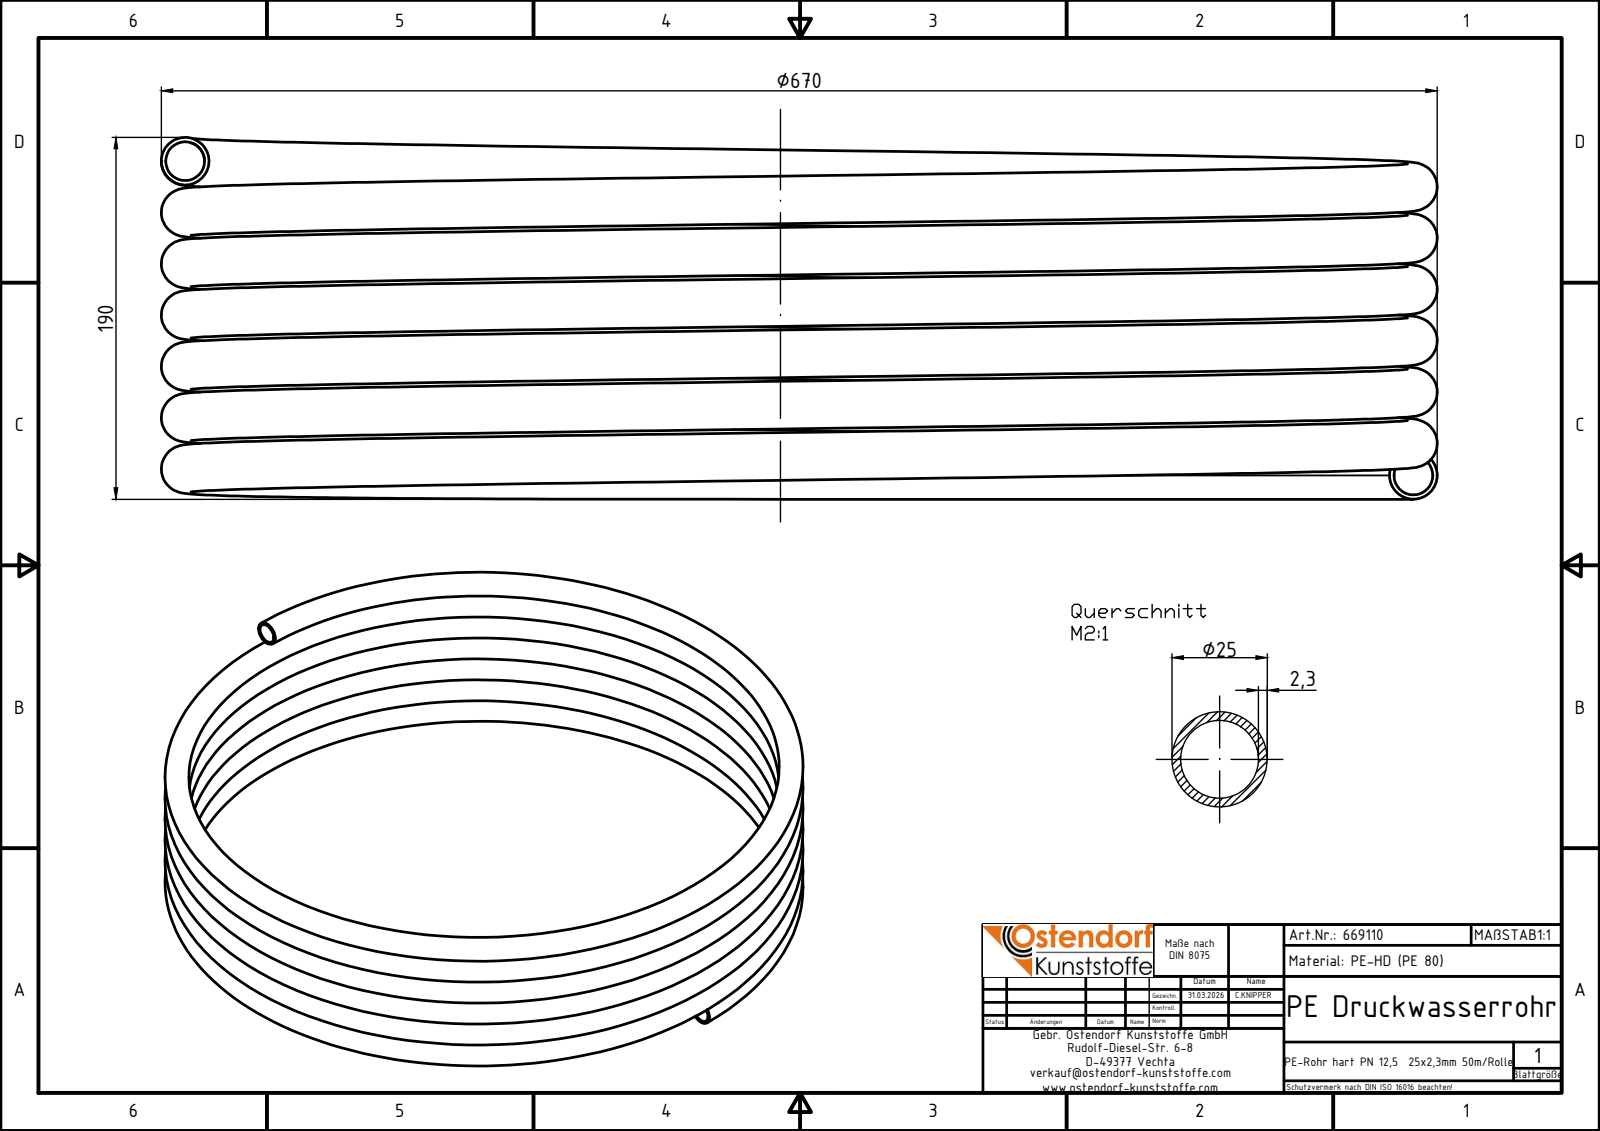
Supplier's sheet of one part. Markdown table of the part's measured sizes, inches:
| quantity | value |
| --- | --- |
| part name | 669110z |
| STEP written by | Autodesk Inventor 2024 (AUTOMOTIVE_DESIGN) |
| units | inches |
| bodies | 1 solid, 7 faces (3 planar, 0 cylindrical, 4 other) |
| overall size | 26.378 × 26.378 × 7.481 |
| volume | 130.2 in³ |
| surface area | 2 880 in² |
